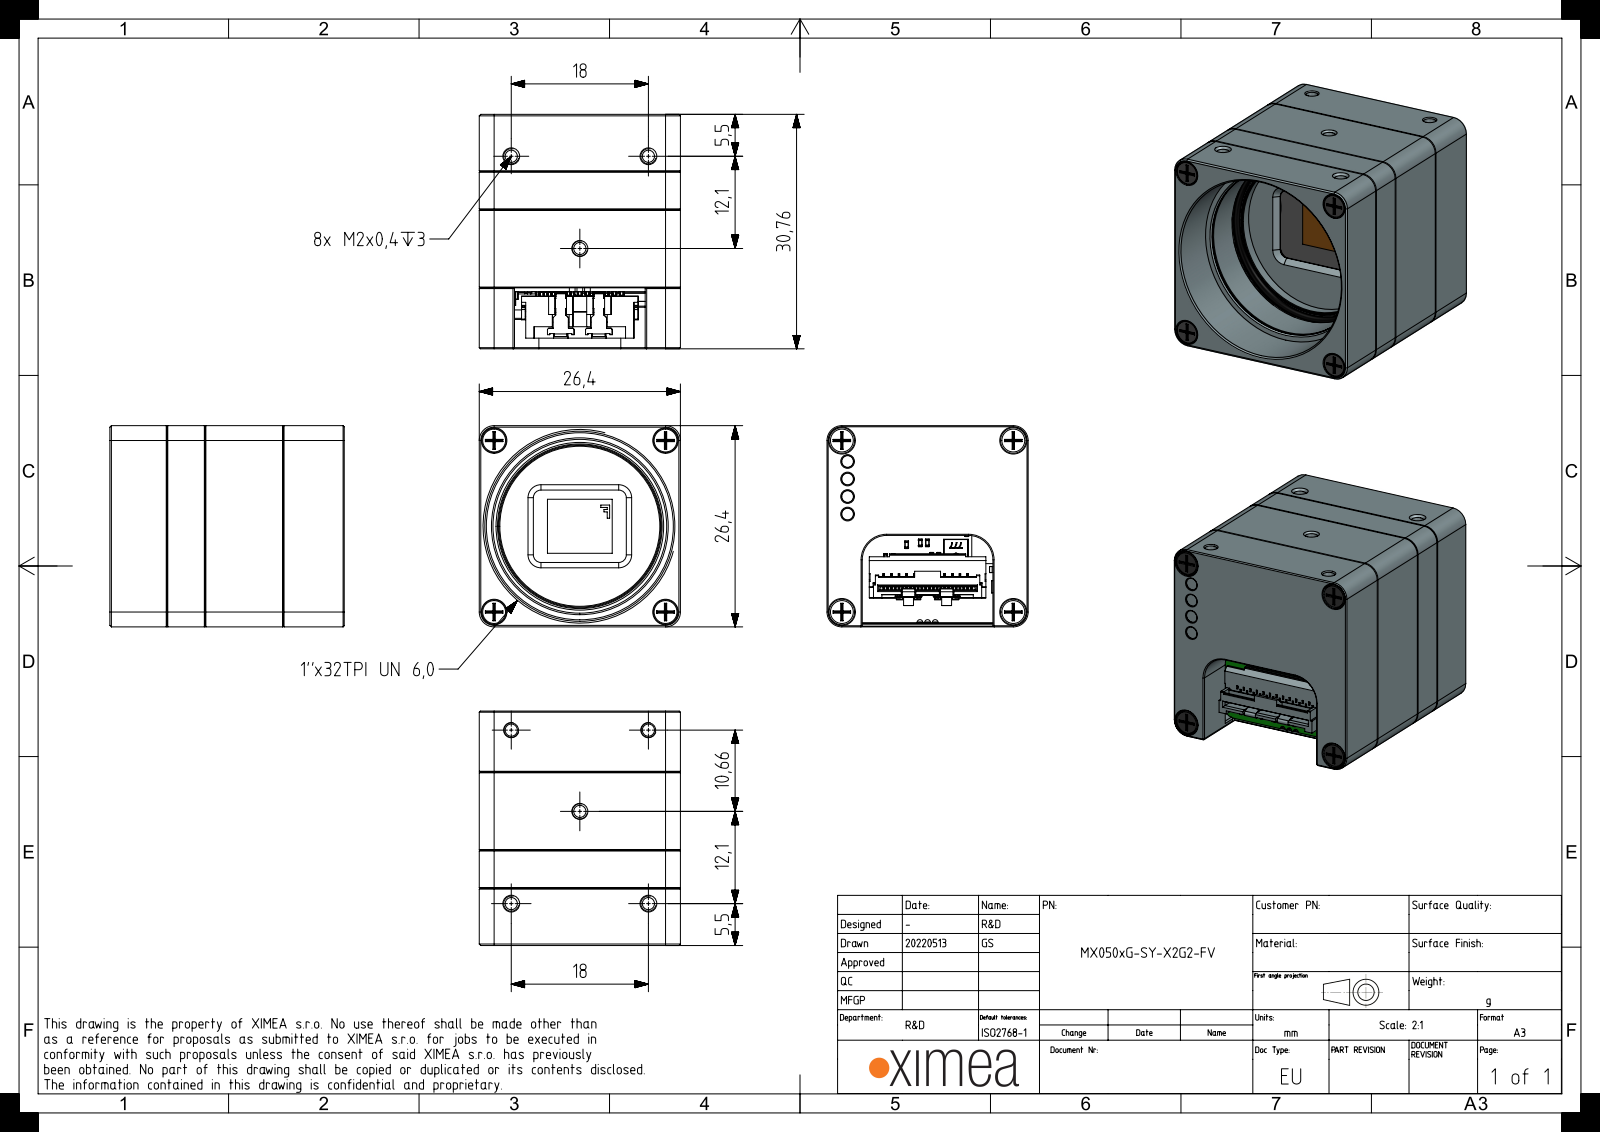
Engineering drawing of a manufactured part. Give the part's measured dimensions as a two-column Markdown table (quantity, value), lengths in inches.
| quantity | value |
| --- | --- |
| part name | SROB-M2x10-CUST; MECH-MX-THERMAL-PAD-10X10; MECH-LIGHTPIPE-1.63x4.14; MX-X2G2-MAIN-FV-PCA (+8 more) |
| STEP written by | SIEMENS PLM Software NX 1907 (AUTOMOTIVE_DESIGN) |
| units | inches |
| bodies | 32 solids, 7513 faces (5230 planar, 2012 cylindrical, 271 other) |
| overall size | 1.211 × 1.039 × 1.039 |
| volume | 0.636 in³ |
| surface area | 27.28 in² |
| round holes (diameter × count) | 0.063 × 13, 0.035 × 4, 0.071 × 4, 0.079 × 4, 0.083 × 4, 0.118 × 4, 0.126 × 4, 0.132 × 4, 0.051 × 2, 0.073 × 1, 0.073 × 1, 0.827 × 1 |
| round bosses / shafts (diameter × count) | 0.075 × 4, 0.064 × 4, 0.033 × 4, 0.118 × 2, 0.063 × 2, 0.984 × 1, 0.85 × 1 |
| partial cylindrical surfaces (radius × count) | 0.059 × 19, 0.013 × 16, 0.006 × 14, 0.039 × 14, 0.004 × 12, 0.015 × 12, 0.051 × 8, 0.008 × 5 |
| main face-to-face distances | 0.039, 1.039, 0.138, 0.447, 0.27, 0.304, 0.165, 0.178, 0.408, 0.404 |
| hole center spacings | 0.15, 0.508, 0.626, 0.739, 0.869, 0.886, 1.131, 0.091 |
